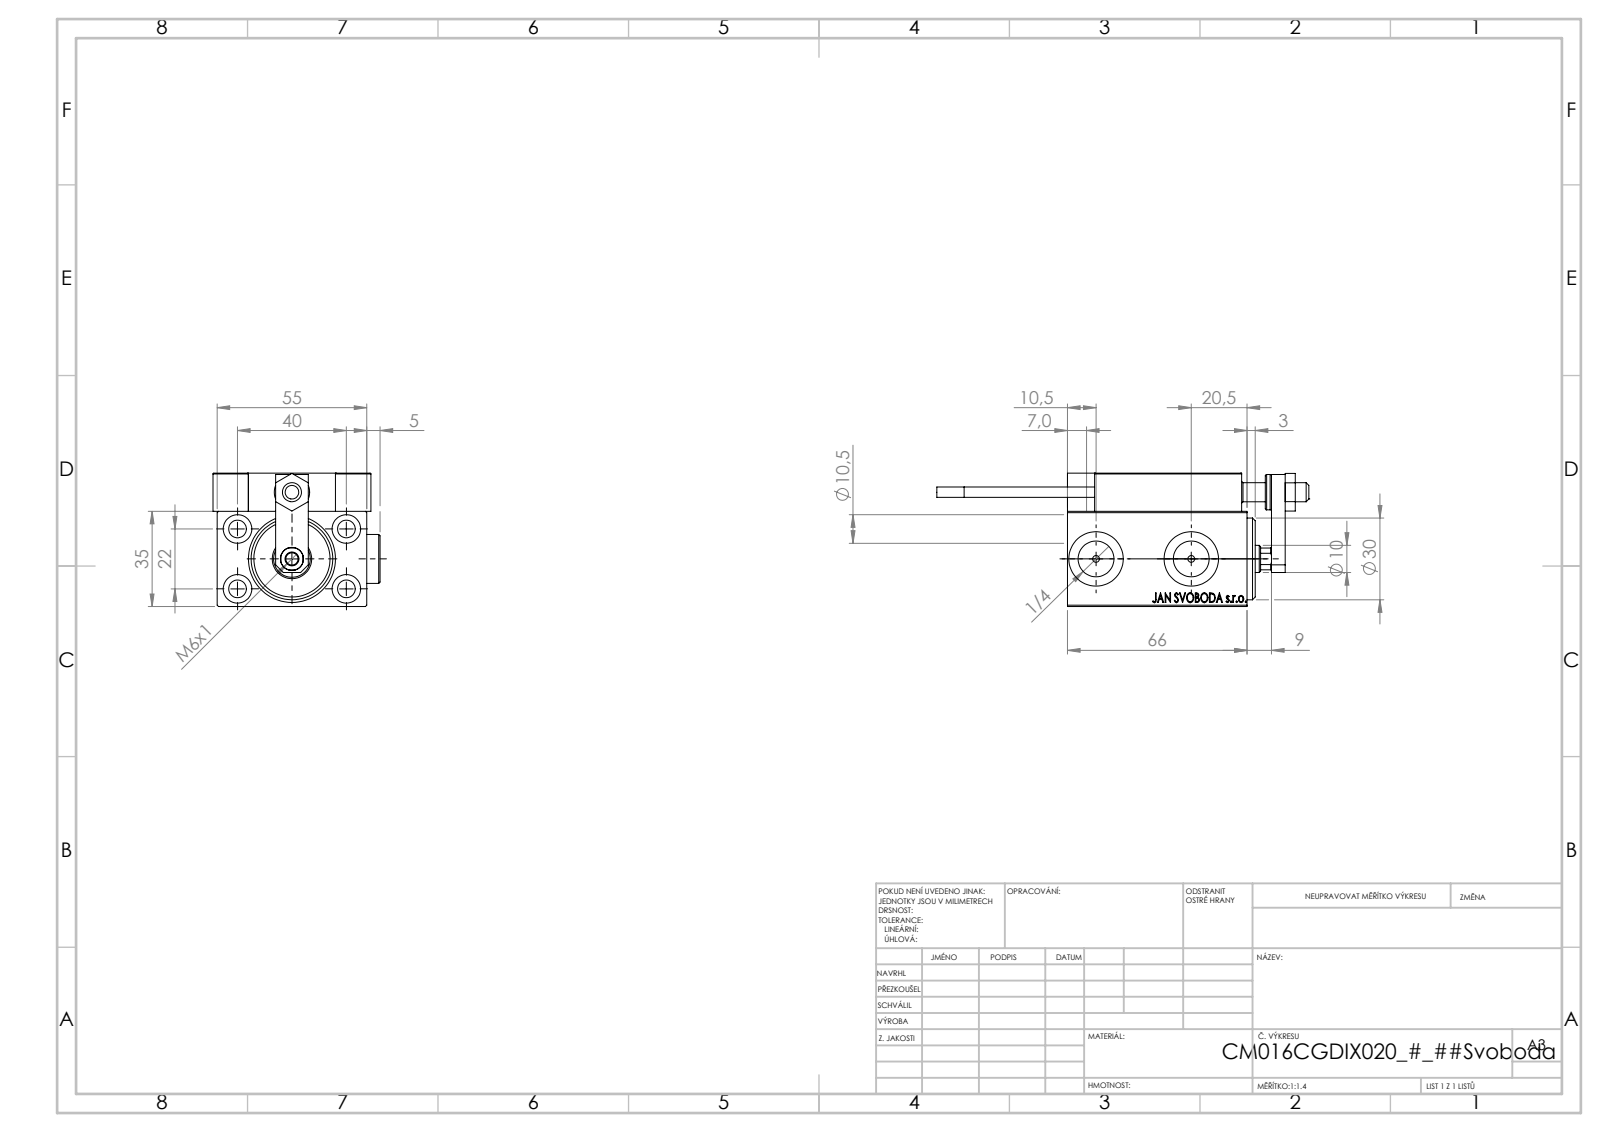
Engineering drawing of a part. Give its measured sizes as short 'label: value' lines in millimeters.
name: SWITCH DIM B,W; V450CM_C_VCP; SWITCH_X_FRONT_BACK; Block (+7 more)
written by: SolidWorks 2019 (CONFIG_CONTROL_DESIGN)
unit: mm
bodies: 25 solids, 1339 faces (595 planar, 206 cylindrical, 538 other)
size: 136.7 × 61.4 × 49
volume: 151 823 mm³; area: 56 370 mm²
holes: 5× ⌀8, 4× ⌀3.2, 4× ⌀4, 4× ⌀6.5, 4× ⌀10.5, 2× ⌀2.5, 2× ⌀5, 2× ⌀13.16, 2× ⌀20, 1× ⌀4.5, 1× ⌀7, 1× ⌀8.5
bosses: 2× ⌀18, 2× ⌀5, 2× ⌀3.8, 1× ⌀13, 1× ⌀11
rounds: 28× R0.3, 2× R3, 1× R4.5
face distances: 35, 5, 14, 49, 7, 10, 3, 1.5, 54, 55
hole spacings: 22.83, 11.37, 18.11, 20, 22, 24.13, 28.43, 29.59
